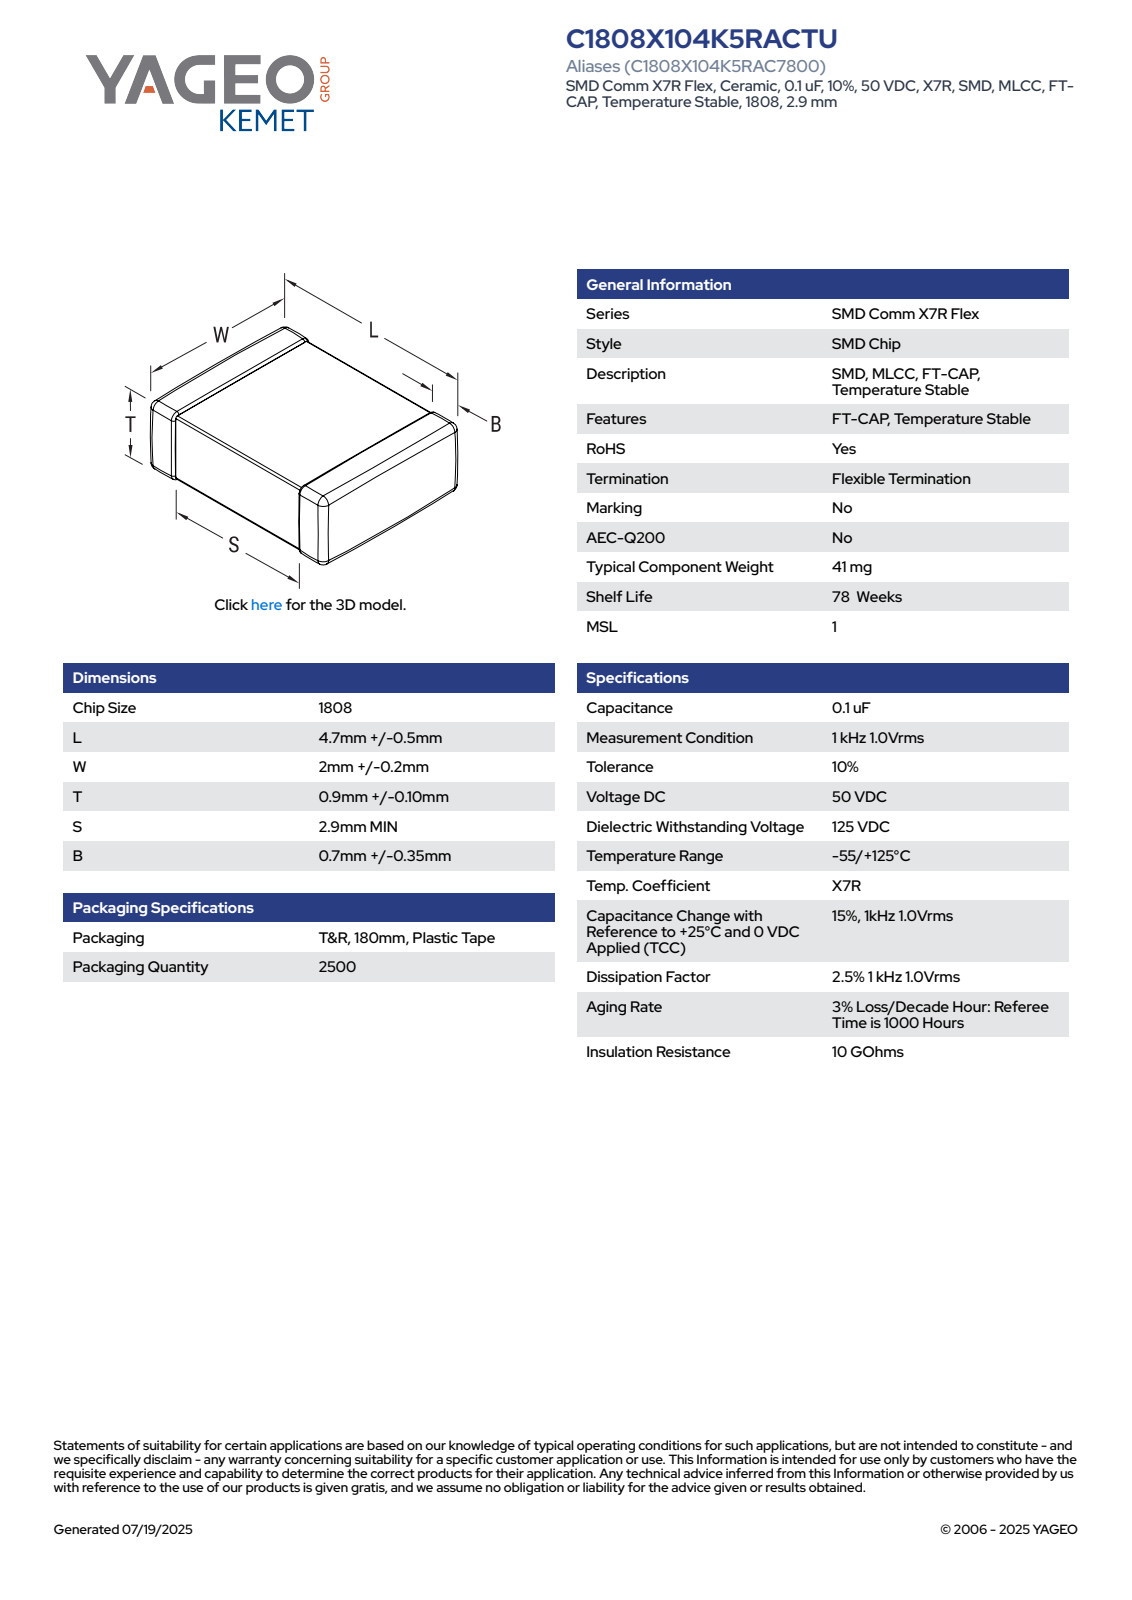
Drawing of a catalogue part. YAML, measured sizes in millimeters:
part_name: "CCS_CCSTD_1808_L5.2W2.2T1B0.7"
step_written_by: "SolidWorks 2021 (AUTOMOTIVE_DESIGN)"
units: millimeters
bodies: {solids: 4, faces: 125, planar: 71, cylindrical: 38, other: 16}
overall_size: [5.2, 2.2, 1]
volume: 11
surface_area: 37
face_to_face_distances: [0.95, 0.9, 1, 2.15, 2.1, 5.2, 2.2, 0.91, 0.96, 0.33]
